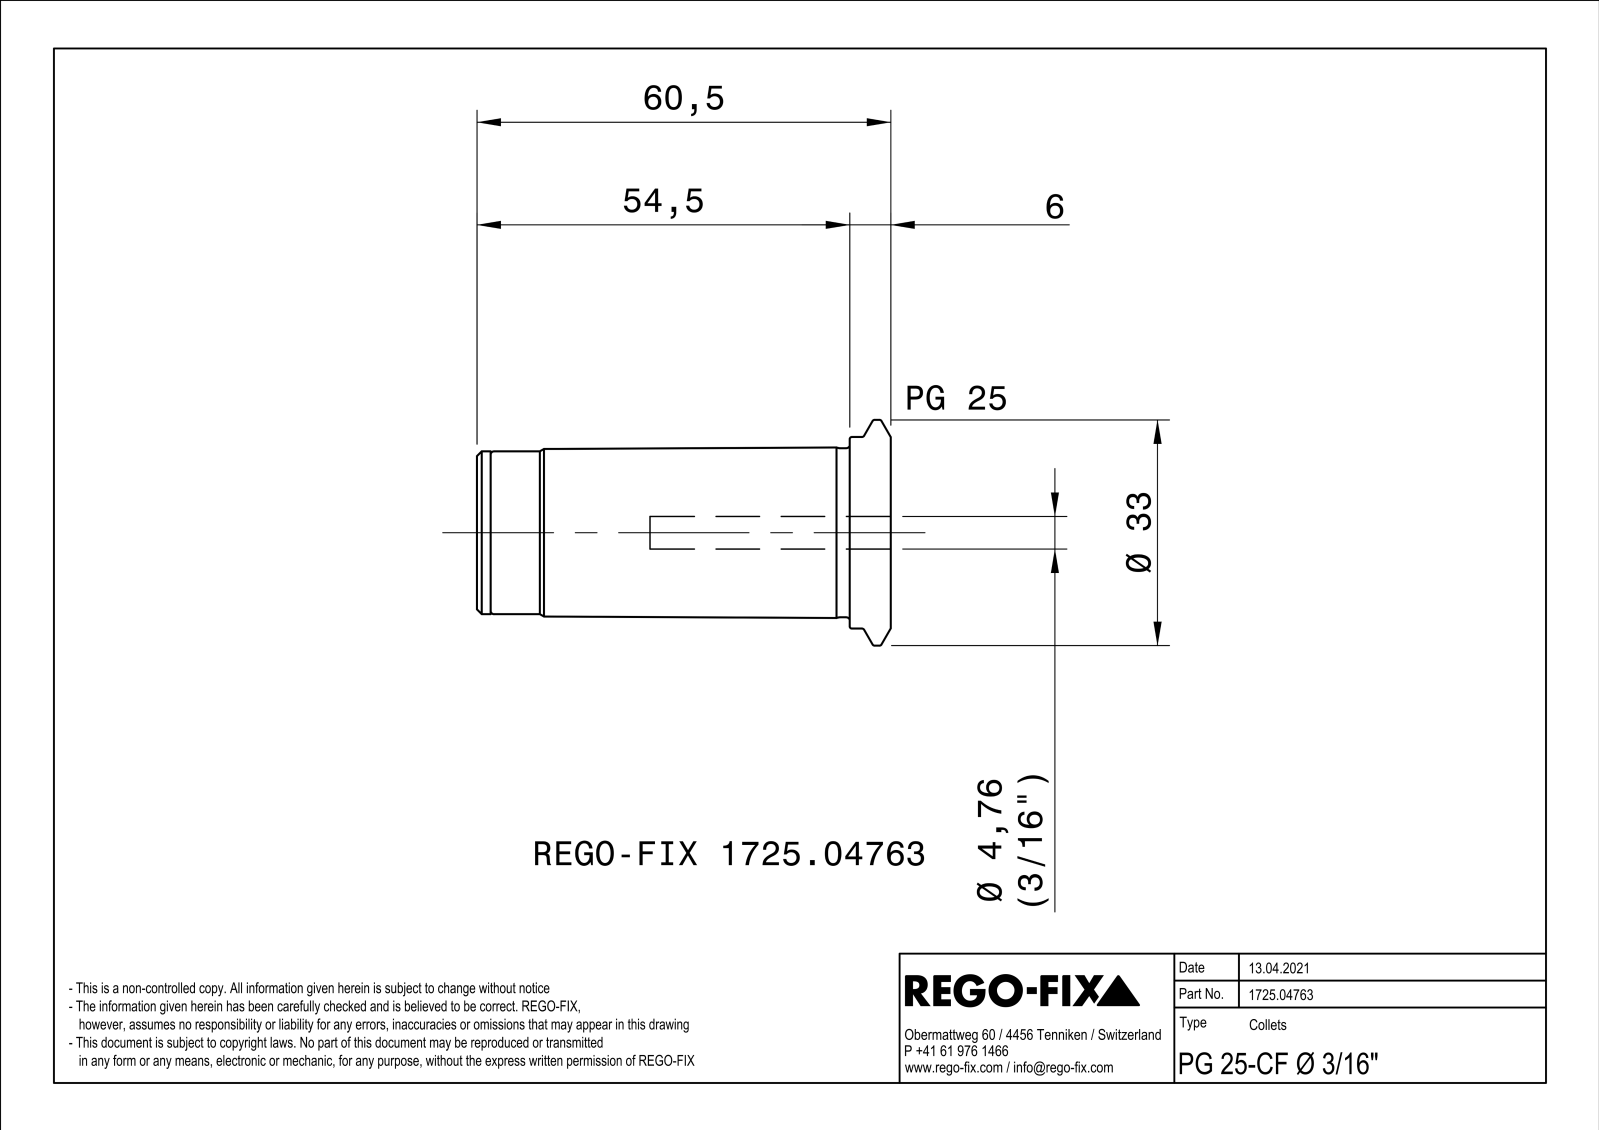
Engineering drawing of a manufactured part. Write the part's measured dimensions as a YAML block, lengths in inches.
part_name: "NOCUT"
step_written_by: "SIEMENS PLM Software Solid Edge ST10 (AUTOMOTIVE_DESIGN)"
units: inches
bodies: {solids: 1, faces: 105, planar: 23, cylindrical: 34, other: 48}
overall_size: [2.382, 1.299, 1.299]
volume: 1.575
surface_area: 17.19
round_holes:
  - {diameter: 0.098, count: 3}
  - {diameter: 0.205, count: 1}
  - {diameter: 0.272, count: 1}
  - {diameter: 0.323, count: 1}
  - {diameter: 0.354, count: 1}
  - {diameter: 0.824, count: 1}
  - {diameter: 0.874, count: 1}
round_bosses_or_shafts:
  - {diameter: 1.299, count: 1}
  - {diameter: 1.102, count: 1}
  - {diameter: 0.972, count: 1}
  - {diameter: 0.937, count: 1}
  - {diameter: 0.803, count: 1}
  - {diameter: 0.472, count: 1}
partial_cylinders:
  - {radius: 0.03, count: 3}
  - {radius: 0.094, count: 1}
  - {radius: 0.098, count: 1}
face_to_face_distances: [0.039, 2.382, 2.071, 0.311, 2.303, 0.232, 0.079, 1.969, 0.102, 0.335]
hole_center_spacings: [0.305, 0.529, 0.528]
